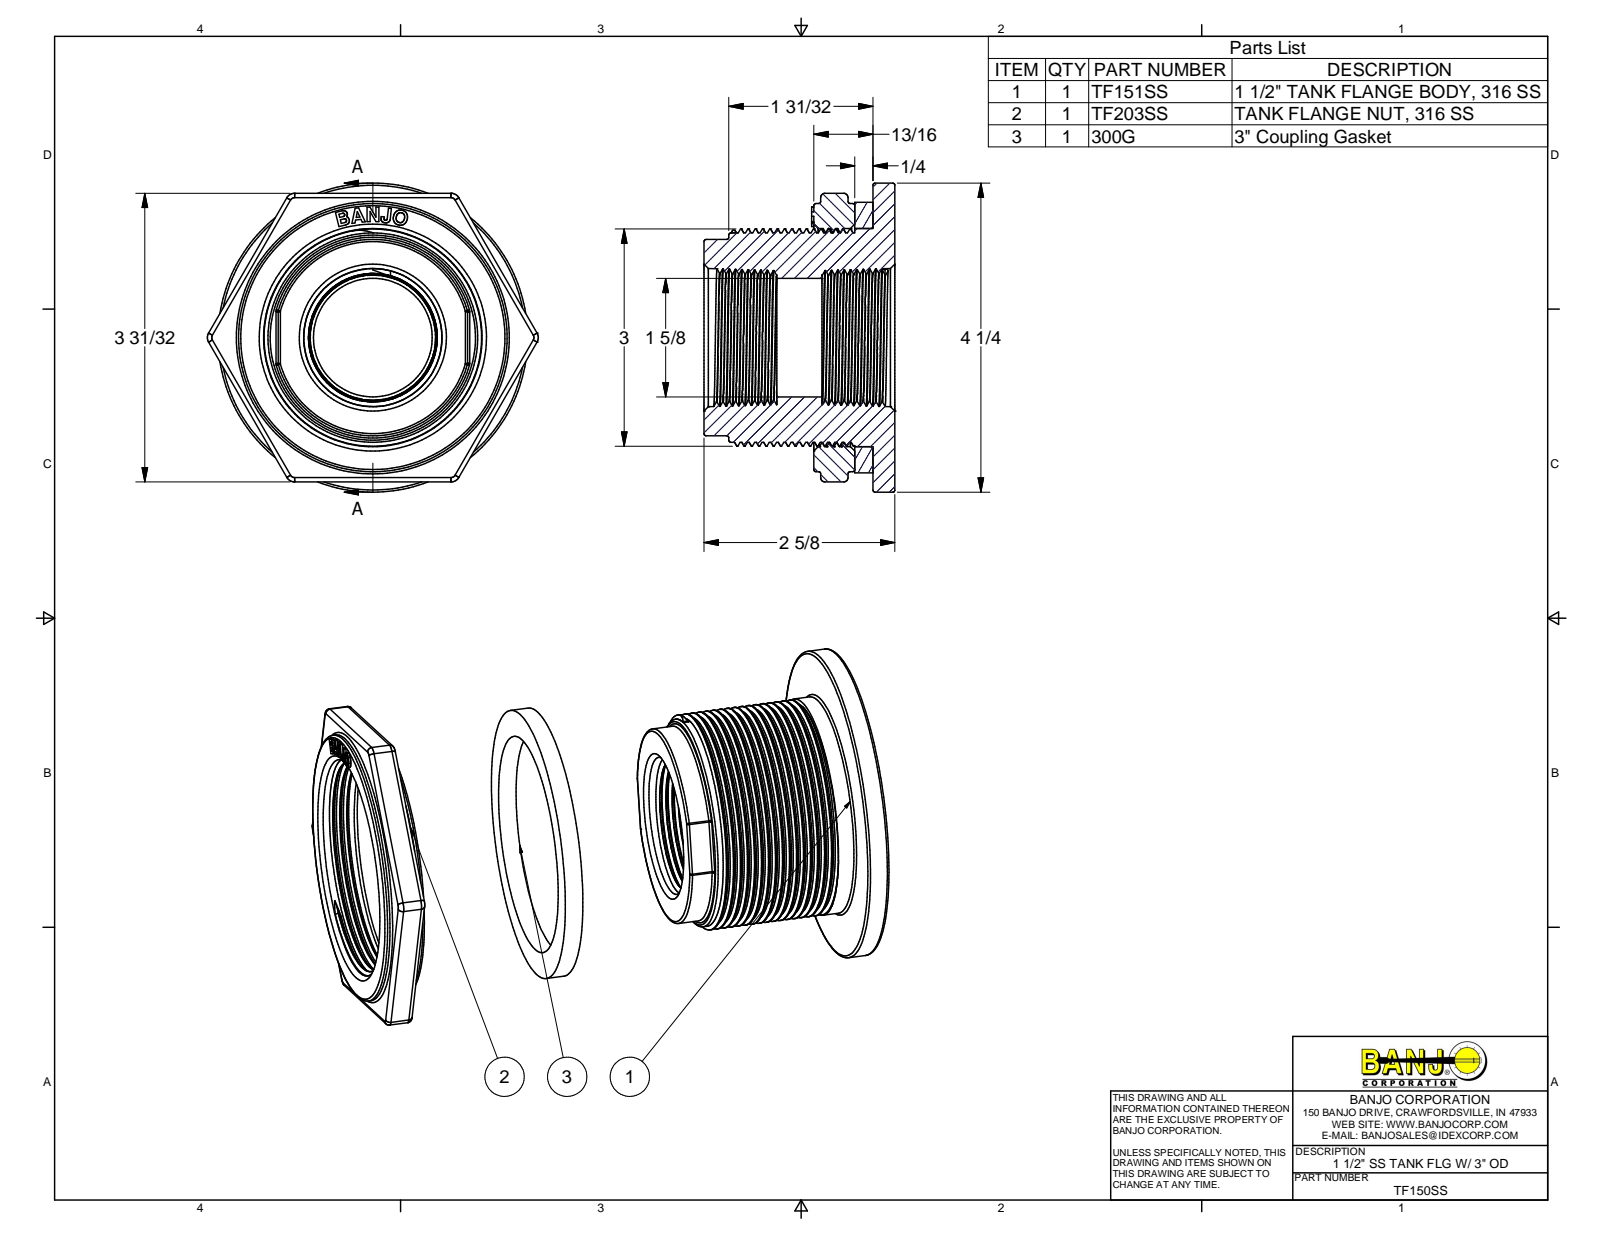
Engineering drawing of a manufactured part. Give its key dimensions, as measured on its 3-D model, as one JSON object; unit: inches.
{"part_name": "TF150SS; TF151SS; TF203SS; 300G", "step_written_by": "Autodesk Inventor 2013 (AUTOMOTIVE_DESIGN)", "units": "inches", "bodies": {"solids": 3, "faces": 216, "planar": 72, "cylindrical": 43, "other": 101}, "overall_size": [4.544, 4.25, 2.62], "volume_in3": 16.59, "surface_area_in2": 118.5, "round_holes": [[1.63, 1], [2.892, 1], [3, 1]], "round_bosses_or_shafts": [[4.25, 1], [3.719, 1], [3.687, 1], [2.987, 1], [2.879, 1], [2.7, 1]], "partial_cylinders_radius": [[0.06, 16], [0.125, 6], [0.03, 4], [0.5, 1]], "face_to_face_distances": [0.3, 0.25, 0.55, 0.094, 0.469, 0.563, 0.813, 1.113, 1.507, 2.07]}
